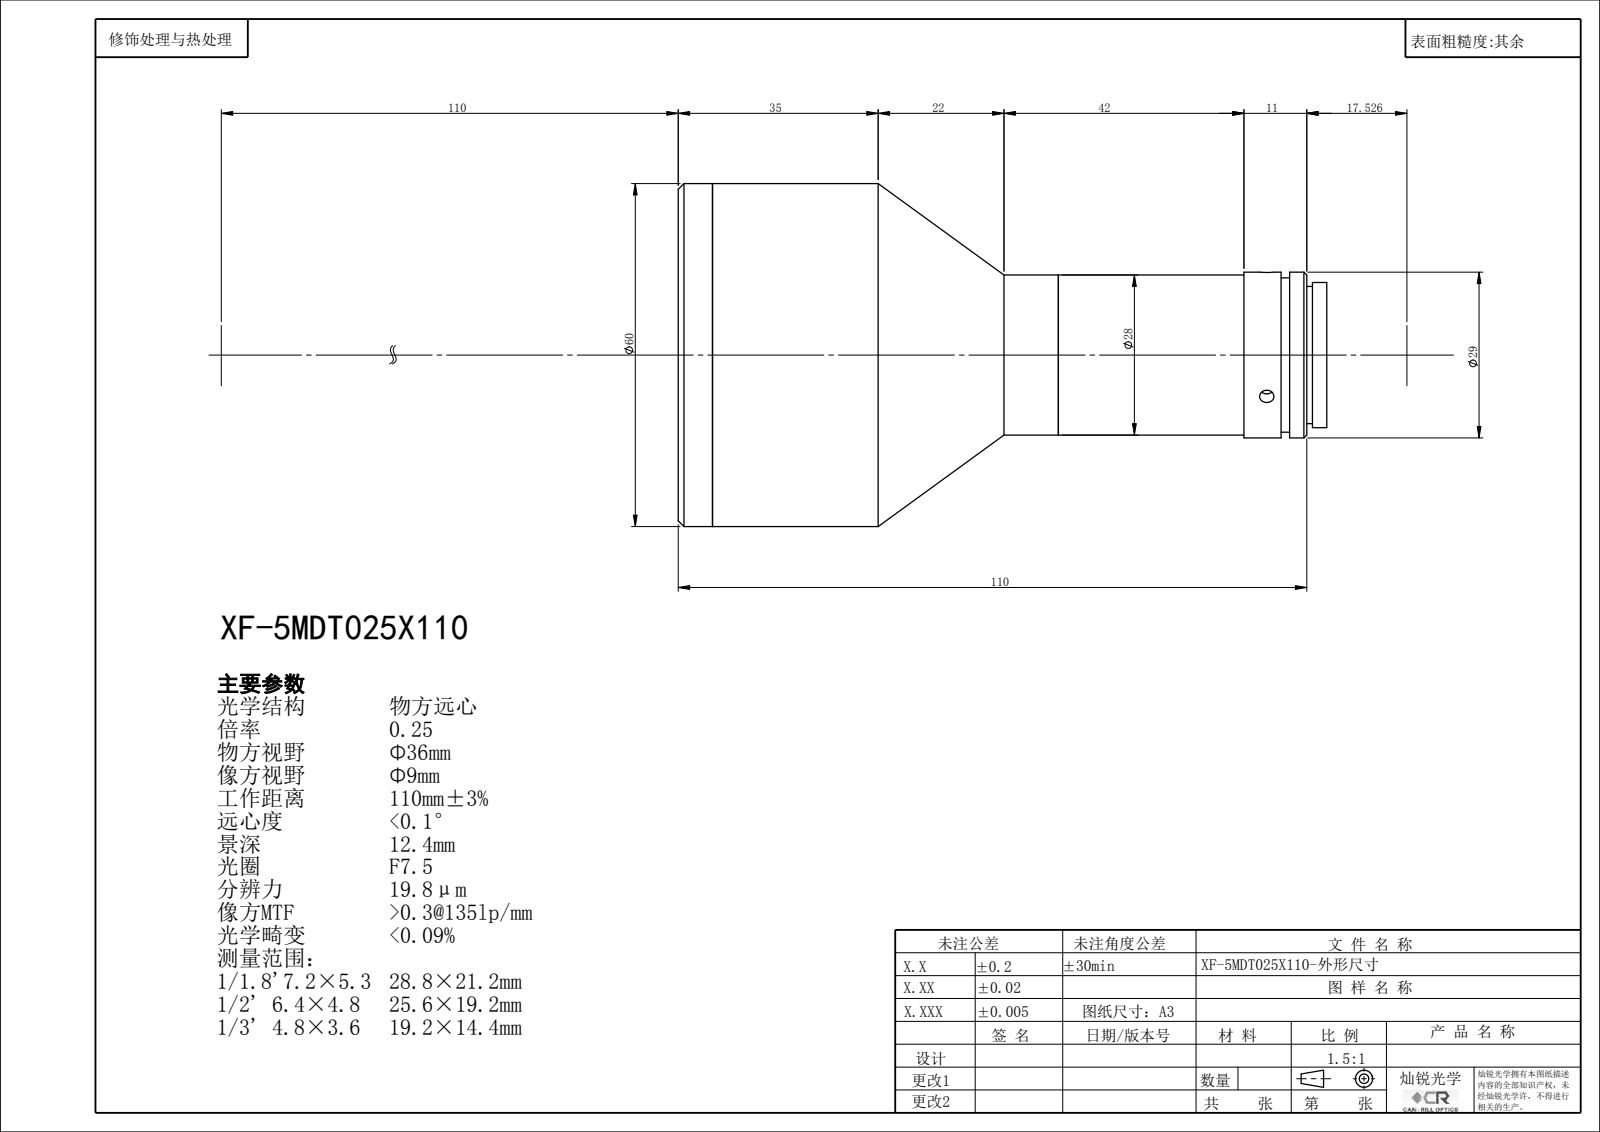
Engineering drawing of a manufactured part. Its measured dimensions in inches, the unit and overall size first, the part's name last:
Units: inches
Overall size (bounding box): 4.47 × 2.362 × 2.362
Round holes (diameter × count): ⌀0.098 ×3, ⌀0.512 ×1, ⌀0.843 ×1, ⌀1.811 ×1, ⌀1.945 ×1, ⌀2.126 ×1
Round bosses / shafts (diameter × count): ⌀2.362 ×1, ⌀1.142 ×1, ⌀1.102 ×1, ⌀1.063 ×1, ⌀1 ×1, ⌀0.945 ×1, ⌀0.787 ×1
Main face-to-face distances: 0.236, 0.094, 0.143, 4.253, 4.159, 4.017, 3.899, 3.805, 3.663, 0.354
Bodies: 0 solids, 67 faces (21 planar, 38 cylindrical, 8 other)
Part name (STEP PRODUCT): XF-5MDT025X110
STEP written by: SolidWorks 2014 (CONFIG_CONTROL_DESIGN)
